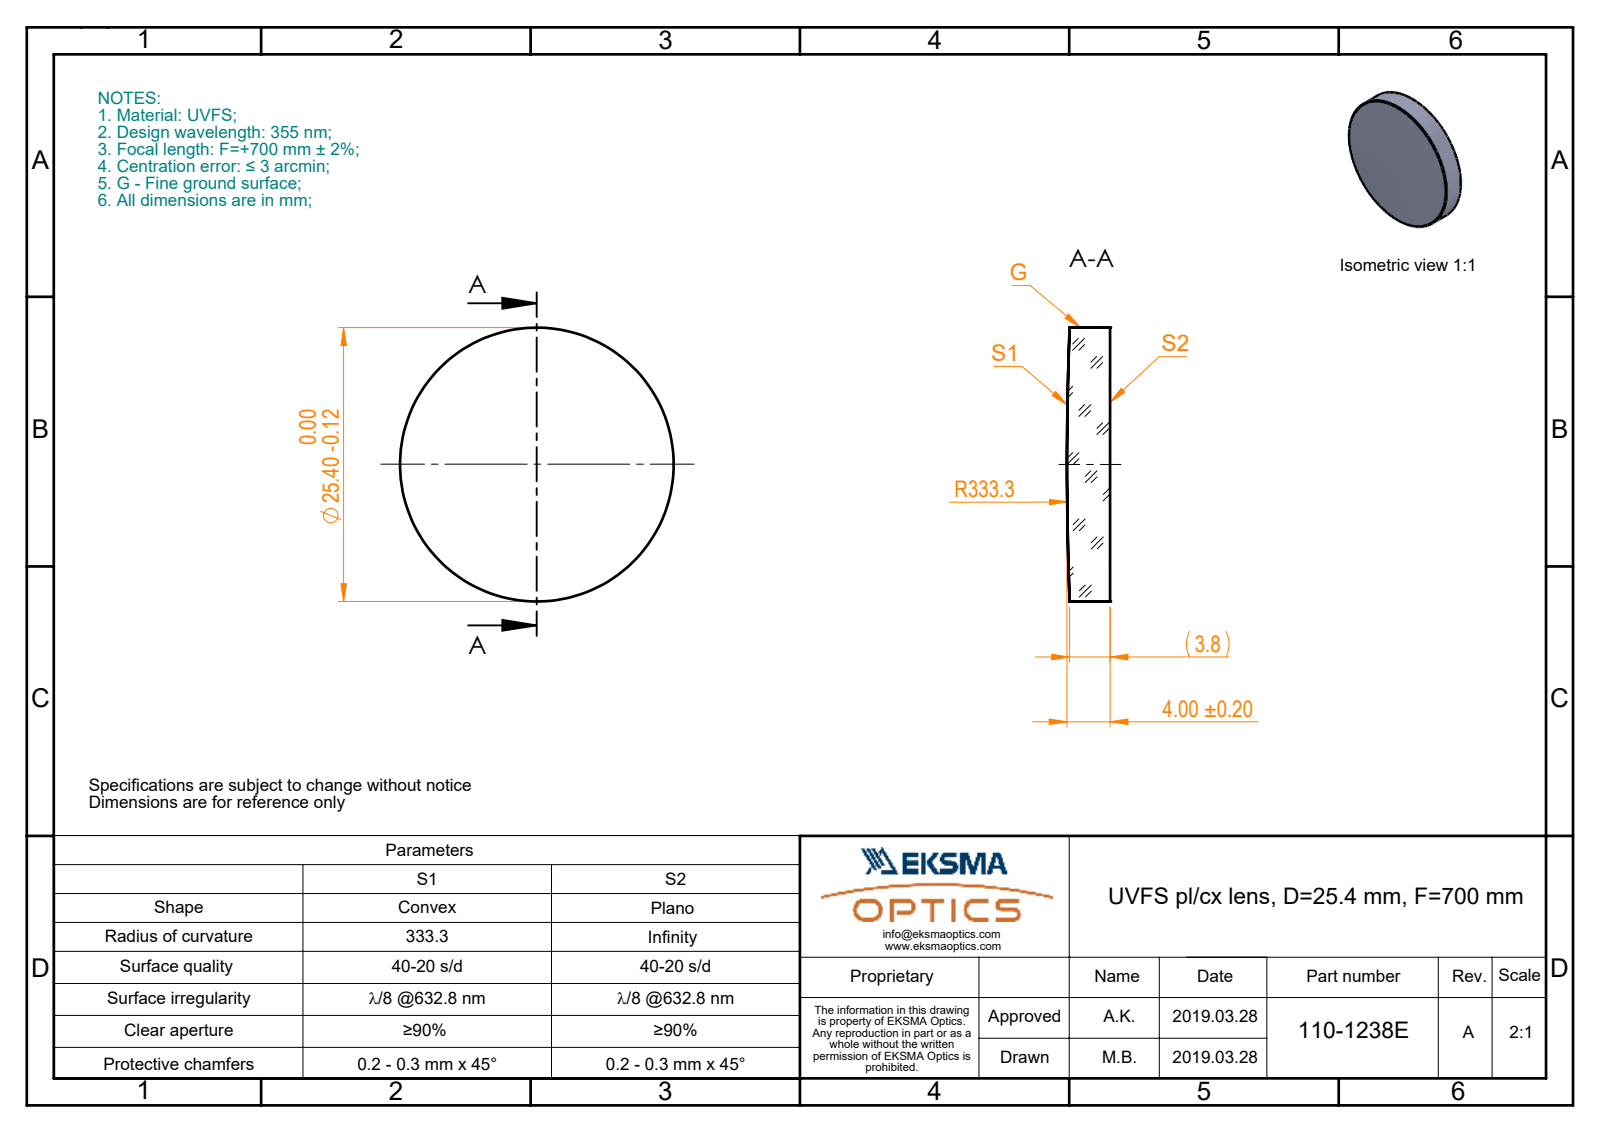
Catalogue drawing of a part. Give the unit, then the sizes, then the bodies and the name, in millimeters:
Units: millimetres
Overall size (bounding box): 25.4 × 25.4 × 4
Round bosses / shafts (diameter × count): ⌀25.4 ×1
Volume: 1 966 mm³ · Surface area: 1 313 mm²
Bodies: 1 solid, 5 faces (1 planar, 2 cylindrical, 2 other)
Part name (STEP PRODUCT): 110-1238E UVFS pl-cx 25.4 F700
STEP written by: SolidWorks 2017 (CONFIG_CONTROL_DESIGN)
